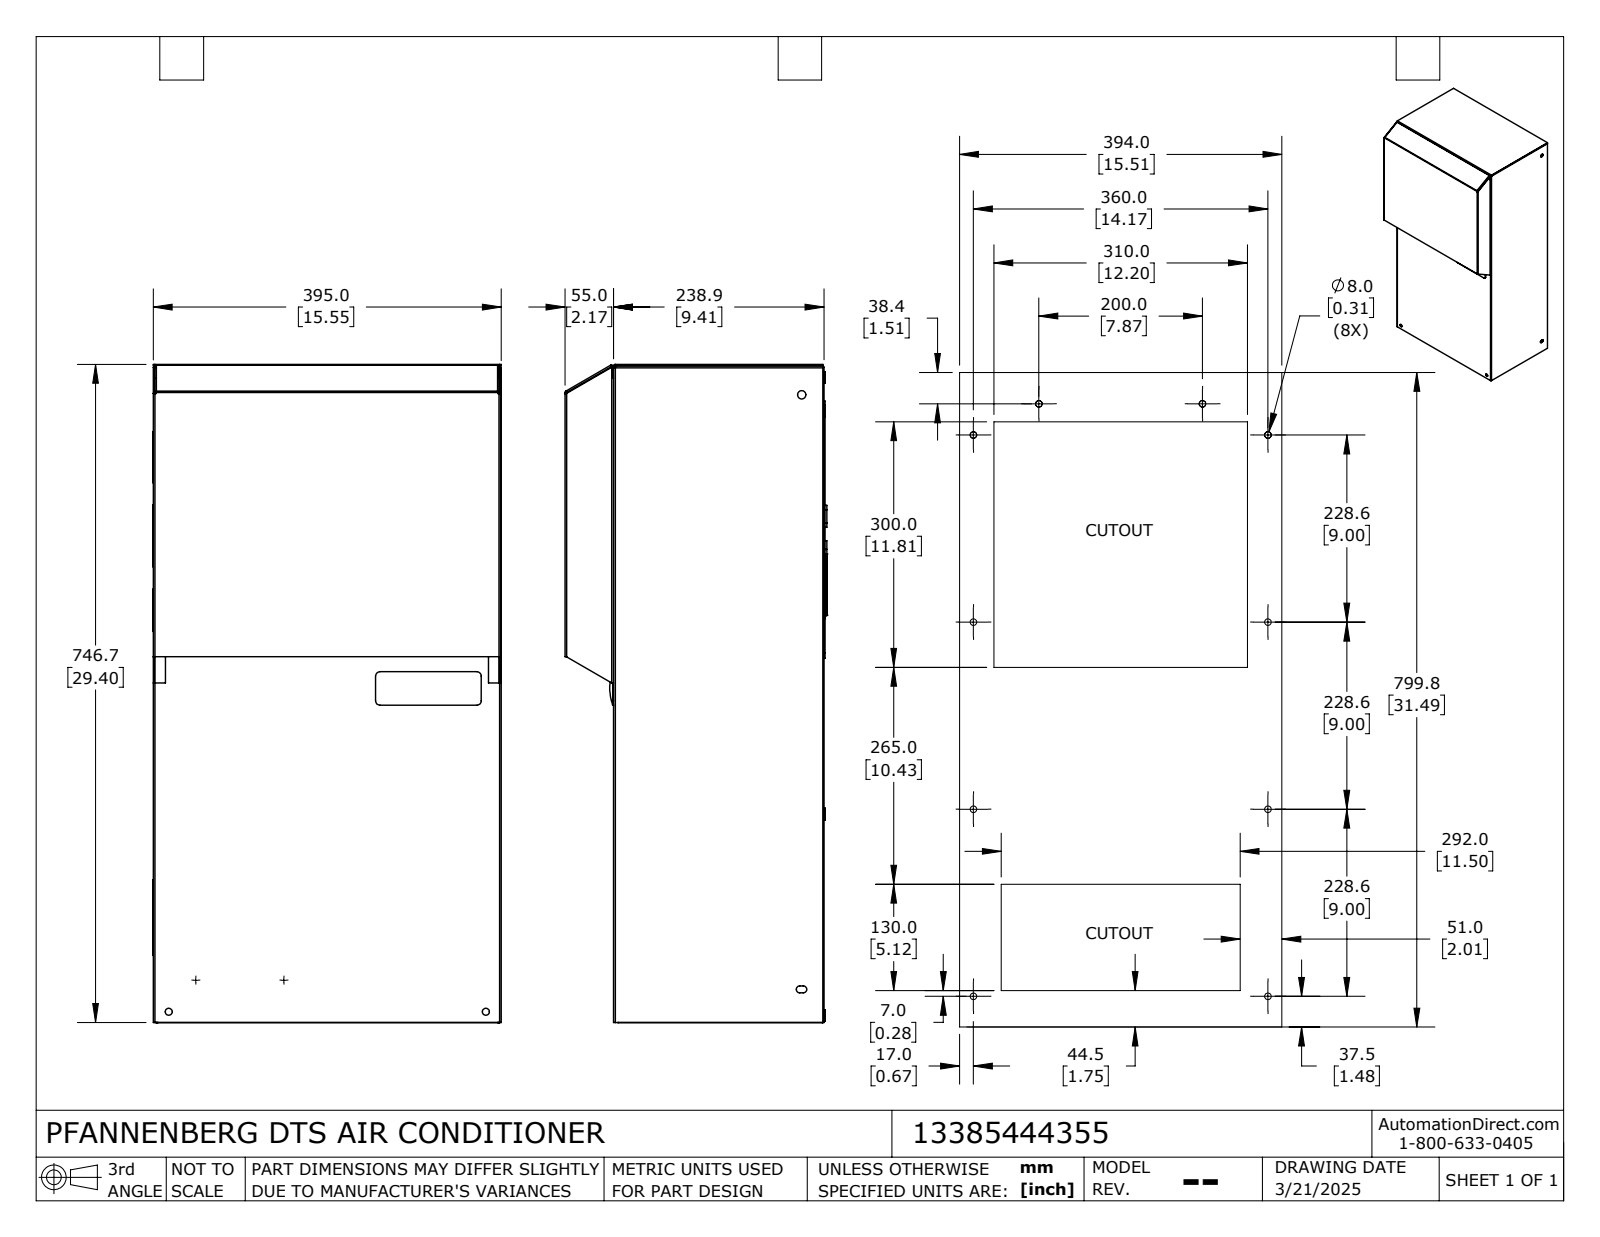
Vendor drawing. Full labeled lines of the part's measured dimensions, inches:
Part name (STEP PRODUCT): 13385444355_Default
STEP written by: SolidWorks 2024 (CONFIG_CONTROL_DESIGN)
Units: inches
Bodies: 1 solid, 1498 faces (764 planar, 713 cylindrical, 21 other)
Overall size (bounding box): 29.397 × 15.571 × 11.698
Volume: 4 282 in³ · Surface area: 4 274 in²
Round holes (diameter × count): ⌀0.165 ×19, ⌀0.283 ×10, ⌀0.163 ×8, ⌀0.157 ×6, ⌀0.197 ×4, ⌀0.236 ×2, ⌀0.315 ×2, ⌀0.437 ×2, ⌀0.118 ×1, ⌀0.318 ×1, ⌀0.375 ×1, ⌀0.825 ×1
Round bosses / shafts (diameter × count): ⌀0.512 ×10
Partial cylindrical surfaces — rounded edges, fillets, slot ends (radius × count): R0.125 ×140, R0.112 ×129, R0.079 ×12, R0.197 ×12, R0.113 ×11, R0.198 ×10, R0.031 ×8, R0.076 ×8
Main face-to-face distances: 0.03, 0.078, 0.048, 9.278, 9.307, 9.355, 0.05, 9.327, 9.357, 9.405
Hole centre spacings: 7.802, 4.398, 5.906, 7.874, 14.744, 26.359, 0.03, 0.035
